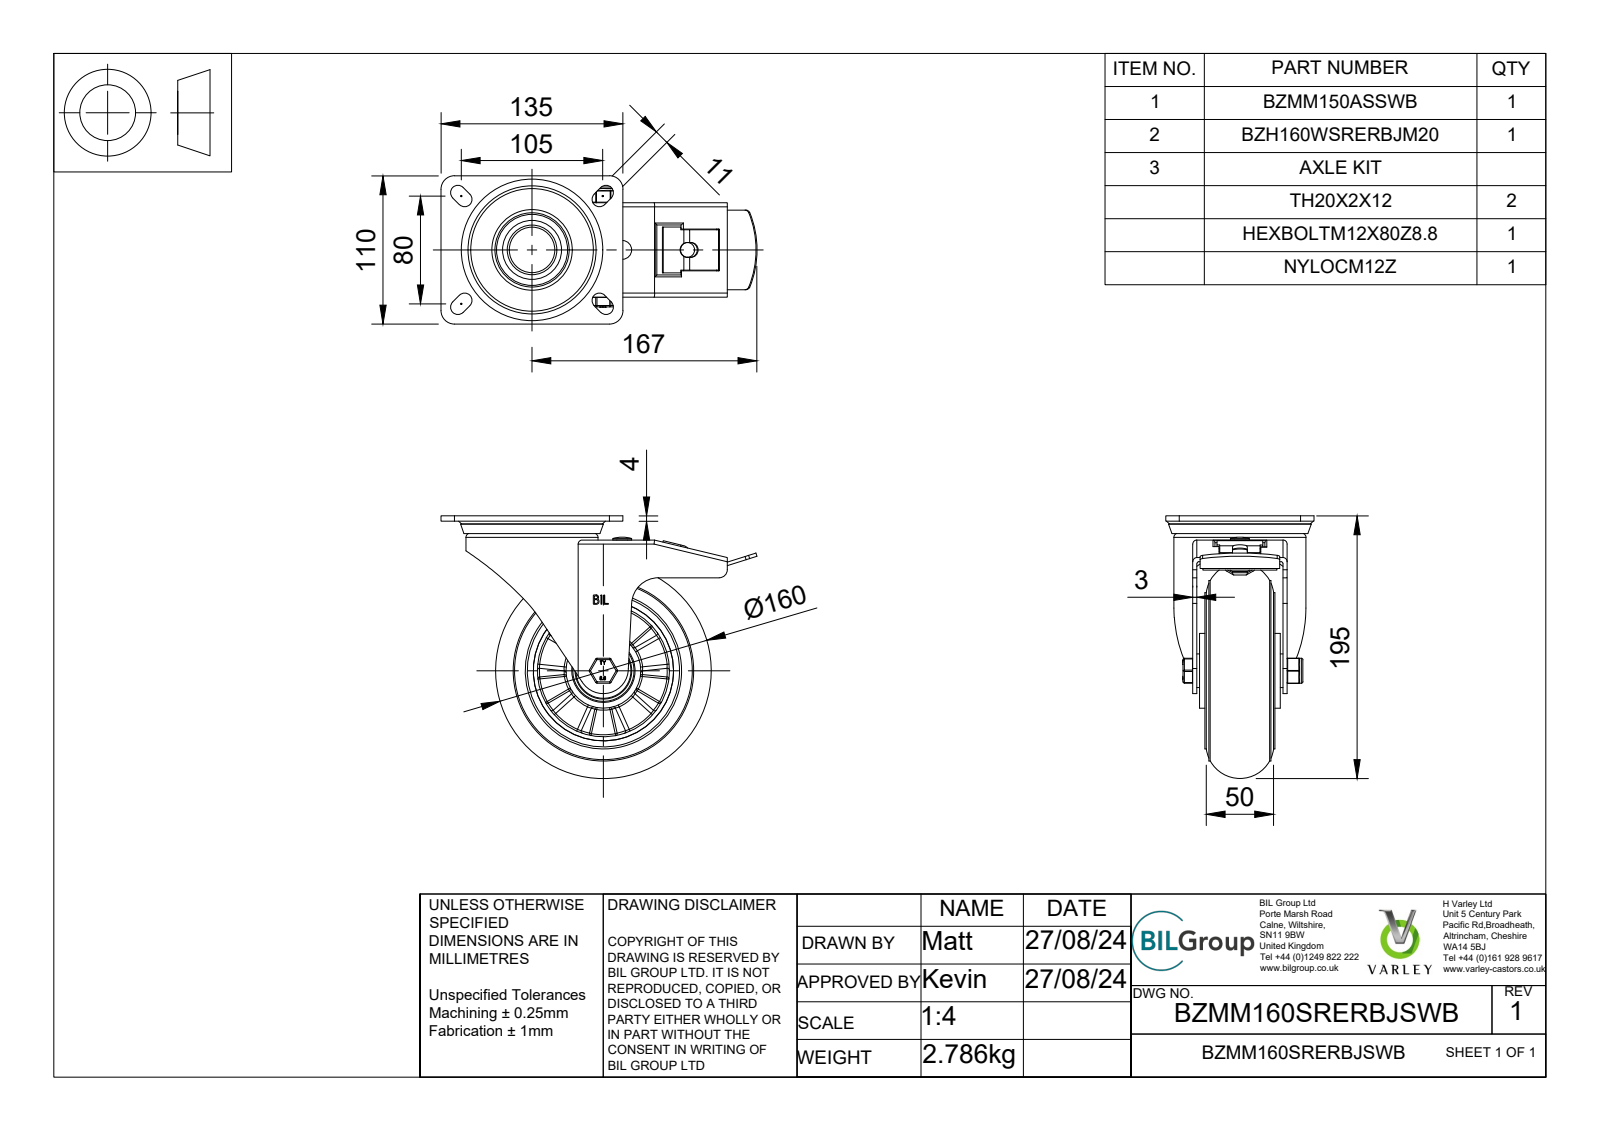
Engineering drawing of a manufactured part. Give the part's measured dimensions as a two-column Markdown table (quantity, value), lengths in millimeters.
| quantity | value |
| --- | --- |
| part name | BZMM160SRERBJSWB v3; BZMM150ASSWB - 64 v1; ZINC PLATED, PRESSED STEEL TOP PLATE; ZINC PLATED, PRESSED STEEL TOP PLATE Geometry (+7 more) |
| STEP written by | Autodesk Translation Framework v13.14.0.145 (AUTOMOTIVE_DESIGN) |
| units | millimeters |
| bodies | 82 solids, 1514 faces (555 planar, 256 cylindrical, 703 other) |
| overall size | 234.5 × 195 × 110 |
| volume | 847 900 mm³ |
| surface area | 318 777 mm² |
| round holes (diameter × count) | 8 × 1, 11 × 1, 12 × 1, 12.2 × 1, 14 × 1, 20 × 1, 28.5 × 1, 30.8 × 1, 33.75 × 1, 39.75 × 1, 40.3 × 1, 40.5 × 1 |
| round bosses / shafts (diameter × count) | 134 × 1, 116 × 1, 98 × 1, 78 × 1, 55.5 × 1, 50 × 1, 40.8 × 1, 31.3 × 1 |
| partial cylindrical surfaces (radius × count) | 0.5 × 18, 1 × 12, 1.5 × 10, 5.5 × 10, 0.25 × 6, 2.5 × 6, 3 × 6, 10 × 4 |
| main face-to-face distances | 3, 9, 5, 7, 4, 12, 17, 2, 67, 14 |
| hole center spacings | 67 |
